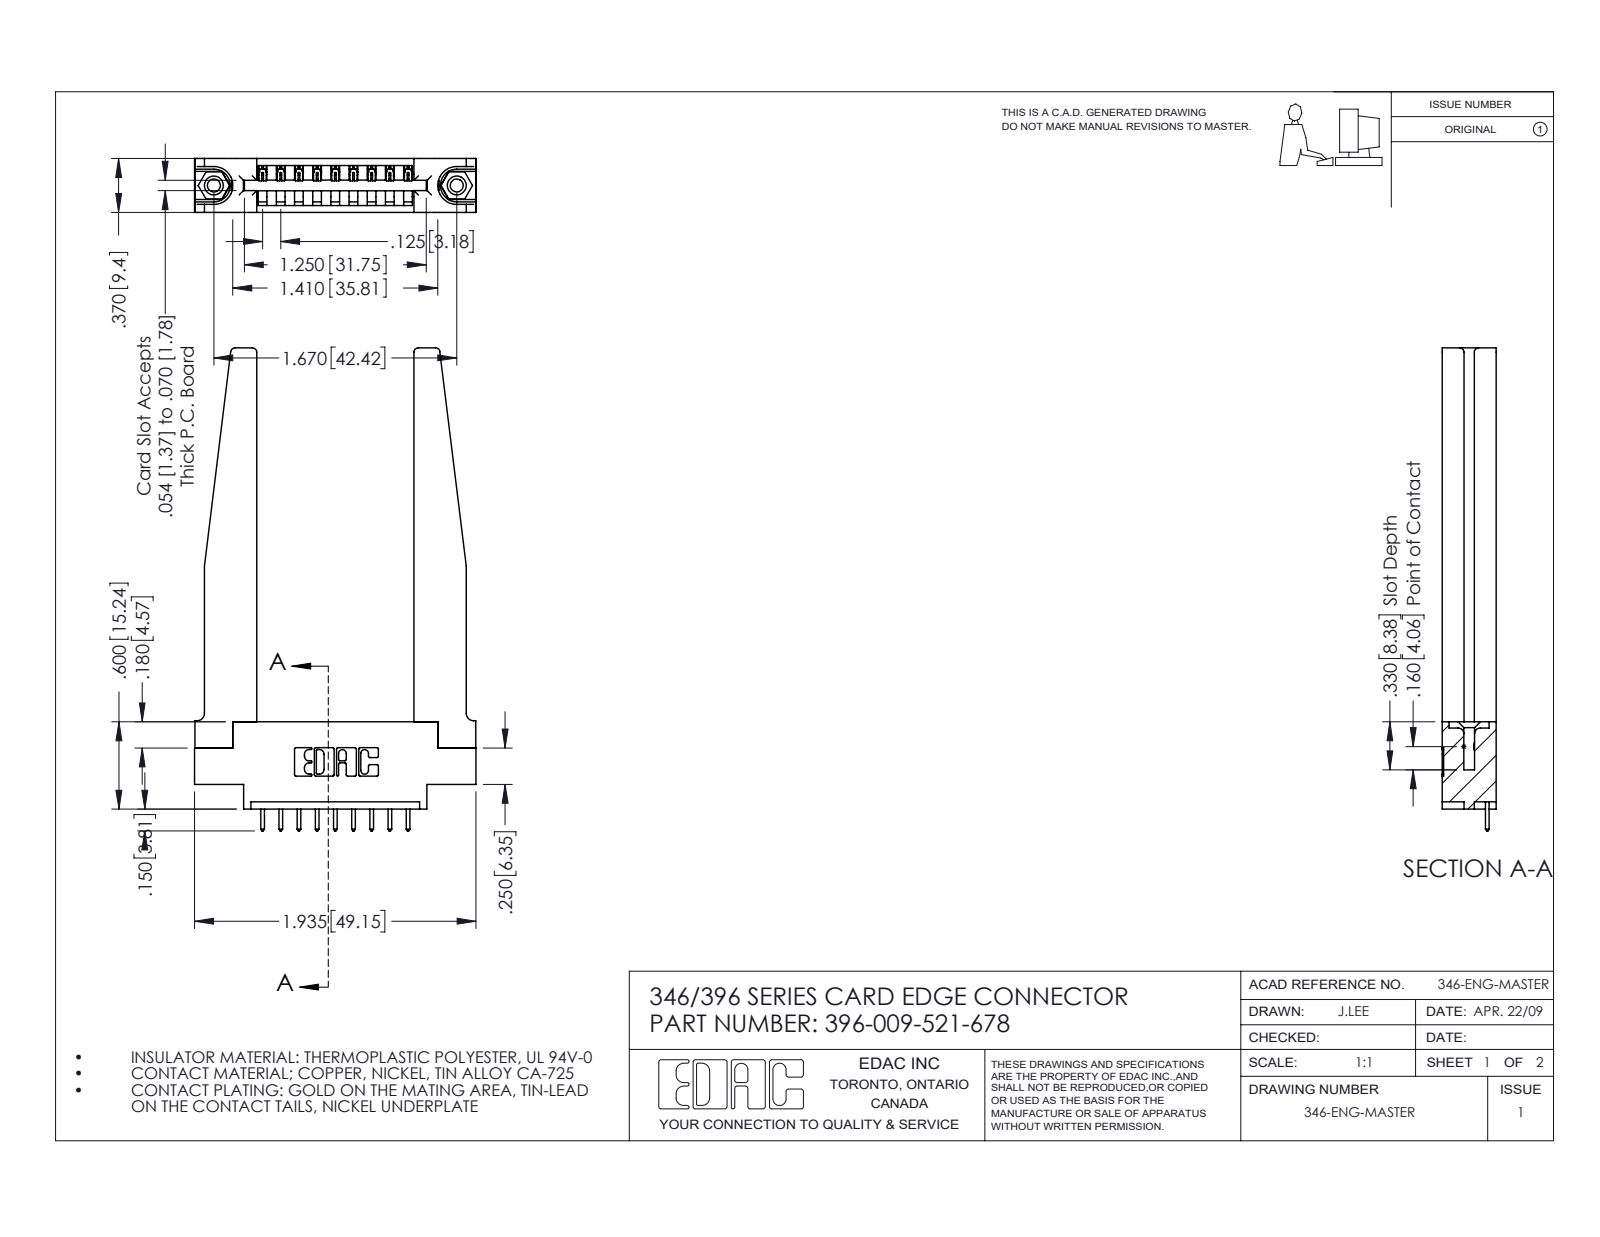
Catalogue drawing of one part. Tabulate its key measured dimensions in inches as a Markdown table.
| quantity | value |
| --- | --- |
| part name | 345-250-001_345-250-001-102; 345-292-001_345-293-121; 396-009-521-678; 346-220-078_345-220-078 (+1 more) |
| STEP written by | SolidWorks 2016 (CONFIG_CONTROL_DESIGN) |
| units | inches |
| bodies | 14 solids, 882 faces (582 planar, 248 cylindrical, 52 other) |
| overall size | 3.32 × 1.935 × 0.37 |
| volume | 0.684 in³ |
| surface area | 18 in² |
| round holes (diameter × count) | 0.089 × 2, 0.125 × 2, 0.156 × 2, 0.064 × 1 |
| round bosses / shafts (diameter × count) | 0.155 × 2 |
| partial cylindrical surfaces (radius × count) | 0.01 × 22, 0.006 × 18, 0.01 × 18, 0.03 × 8, 0.007 × 6, 0.031 × 6, 0.026 × 3, 0.031 × 2 |
| main face-to-face distances | 0.37, 0.15, 0.22, 0.072, 0.148, 0.25, 0.048, 0.322, 0.102, 0.173 |
| hole center spacings | 0.246, 1.465, 1.67 |
